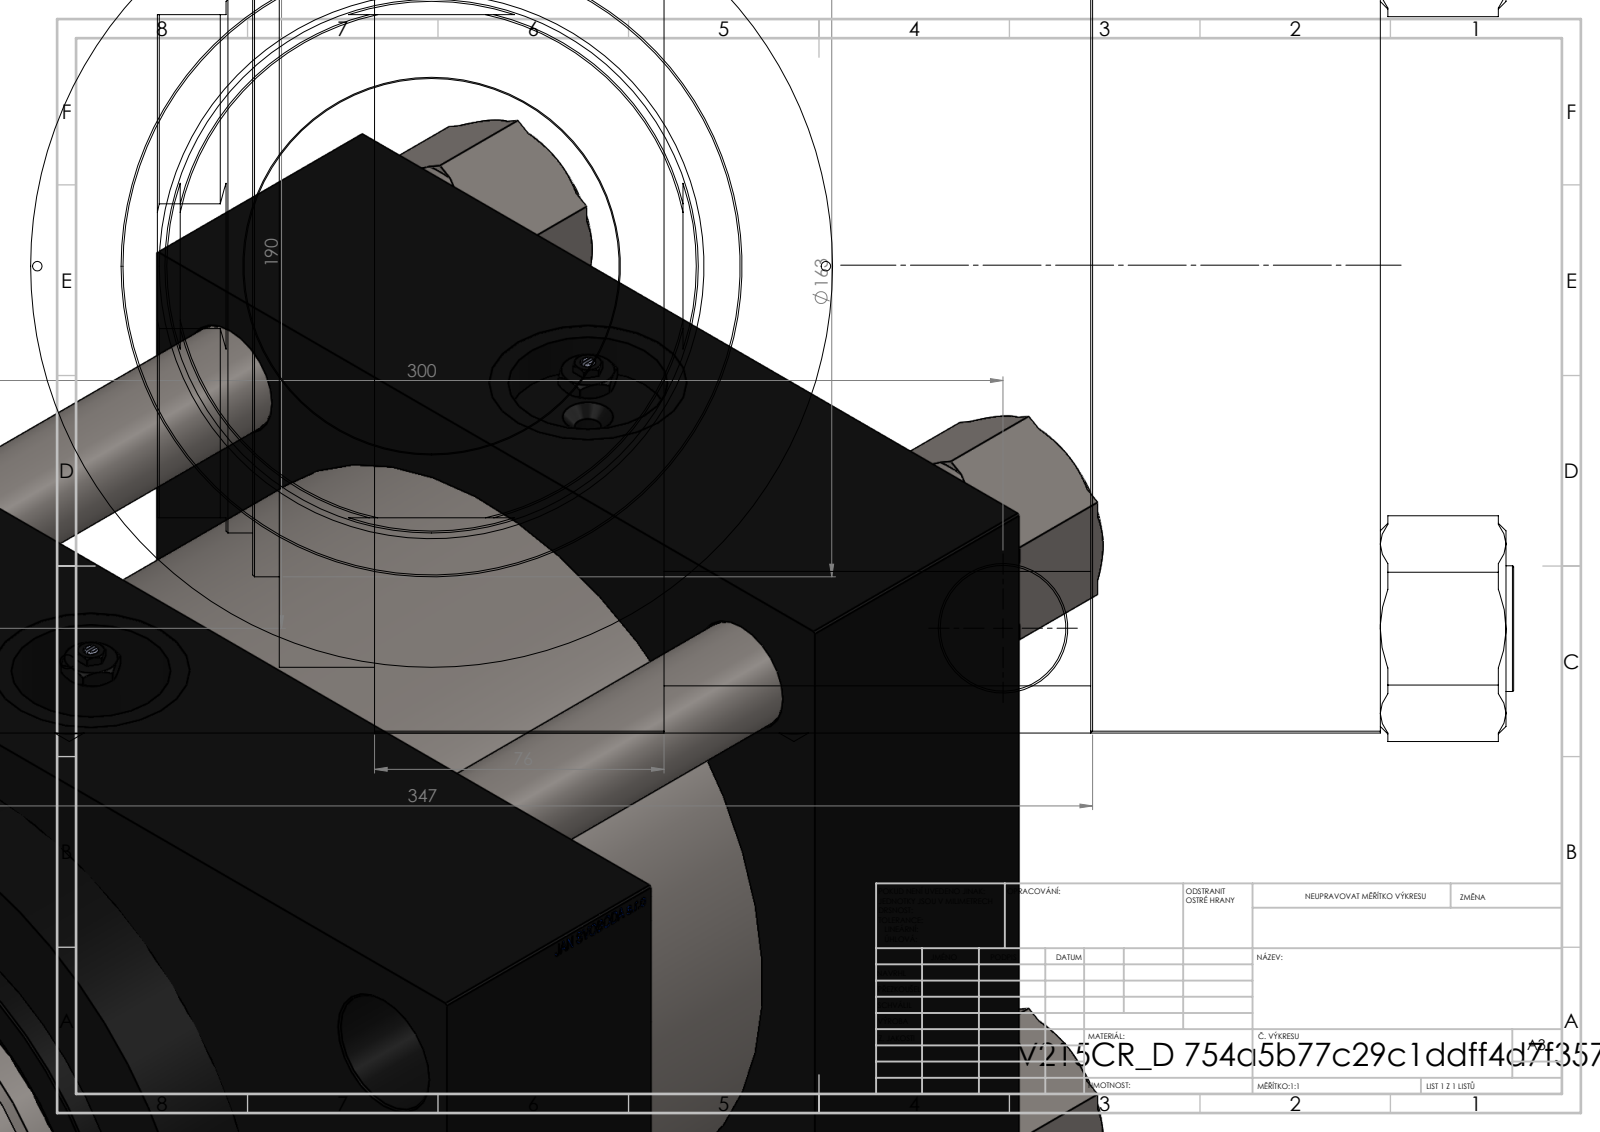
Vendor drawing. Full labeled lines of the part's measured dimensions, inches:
Part name (STEP PRODUCT): V215CR_D_TYCINKA; V215CR_VCP_D; V215CR_D_Body; NUT_M5_D (+2 more)
STEP written by: SolidWorks 2019 (CONFIG_CONTROL_DESIGN)
Units: inches
Bodies: 13 solids, 1254 faces (593 planar, 101 cylindrical, 560 other)
Overall size (bounding box): 14.016 × 13.661 × 10.009
Volume: 908.6 in³ · Surface area: 1 767 in²
Round holes (diameter × count): ⌀1.181 ×4, ⌀1.299 ×4, ⌀1.65 ×4, ⌀2.047 ×4, ⌀0.276 ×3, ⌀0.098 ×2, ⌀3.878 ×1, ⌀5.512 ×1, ⌀5.63 ×1, ⌀5.748 ×1, ⌀7.874 ×1, ⌀8.287 ×1
Round bosses / shafts (diameter × count): ⌀1.299 ×4, ⌀8.11 ×1, ⌀6.417 ×1
Partial cylindrical surfaces — rounded edges, fillets, slot ends (radius × count): R2.677 ×1
Main face-to-face distances: 2.992, 7.402, 9.646, 4.409, 10.394, 9.675, 6.683, 2.273, 0.719, 11.654
Hole centre spacings: 2.161, 3.759, 4.164, 5.295, 6.99, 7.488, 7.79, 8.669
